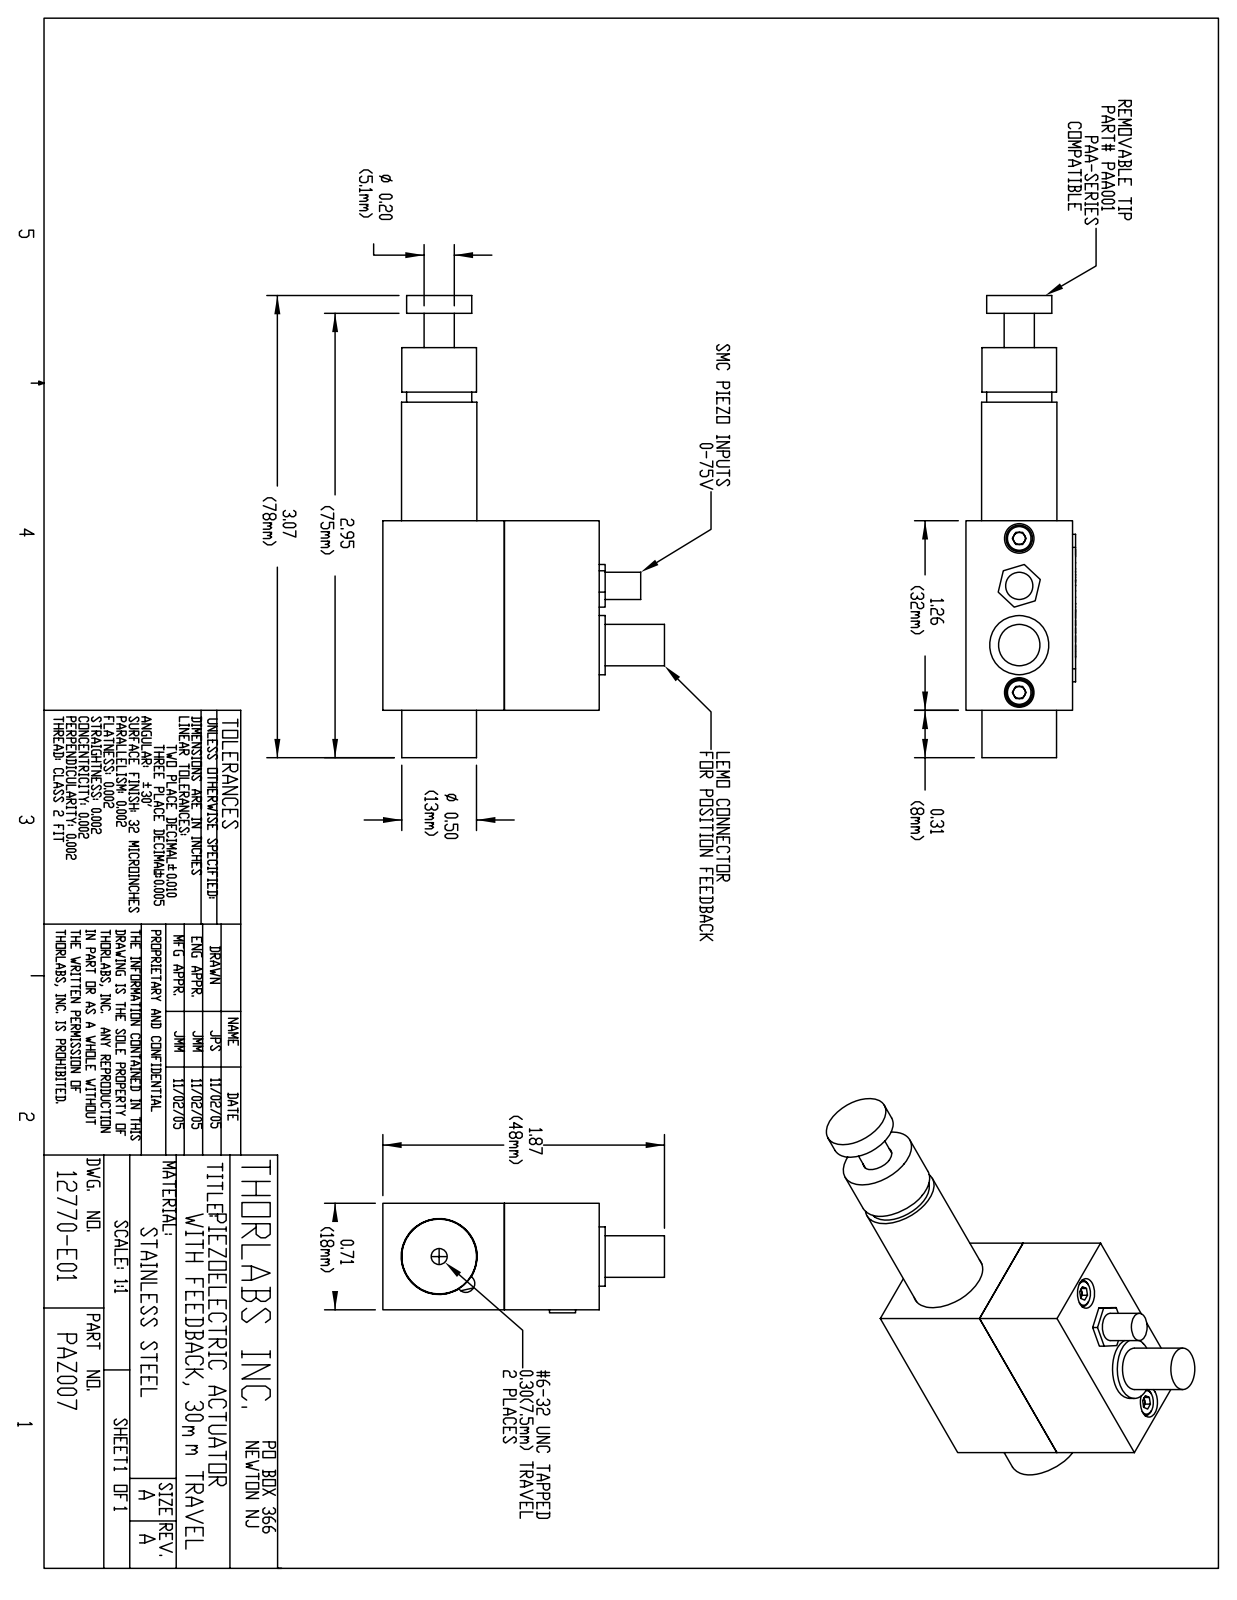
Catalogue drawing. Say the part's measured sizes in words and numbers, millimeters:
The part is named "12770-E0W". Its 3-D file was written by "SolidWorks 2007 (AUTOMOTIVE_DESIGN)". It is 0 solids with 155 faces: 98 planar, 40 cylindrical and 17 other. Overall it measures 78 by 48 by 19.6 millimeters. Round holes: 2 of diameter 2.5, 2 of diameter 5, 1 of diameter 2.7, 1 of diameter 5.3, 1 of diameter 11.4, 1 of diameter 12.8. Round bosses or shafts: 1 of diameter 12.7, 1 of diameter 12.6, 1 of diameter 11, 1 of diameter 10, 1 of diameter 7, 1 of diameter 5.1, 1 of diameter 4.6. Partial cylindrical surfaces (rounded edges, fillets, slot ends): 2 of radius 2.2, 1 of radius 1.5. The main face-to-face distances are 18, 32, 36.5, 16, 20.5, 40, 8, 0.5, 29.2, 61.2. The hole center spacings are 26.
